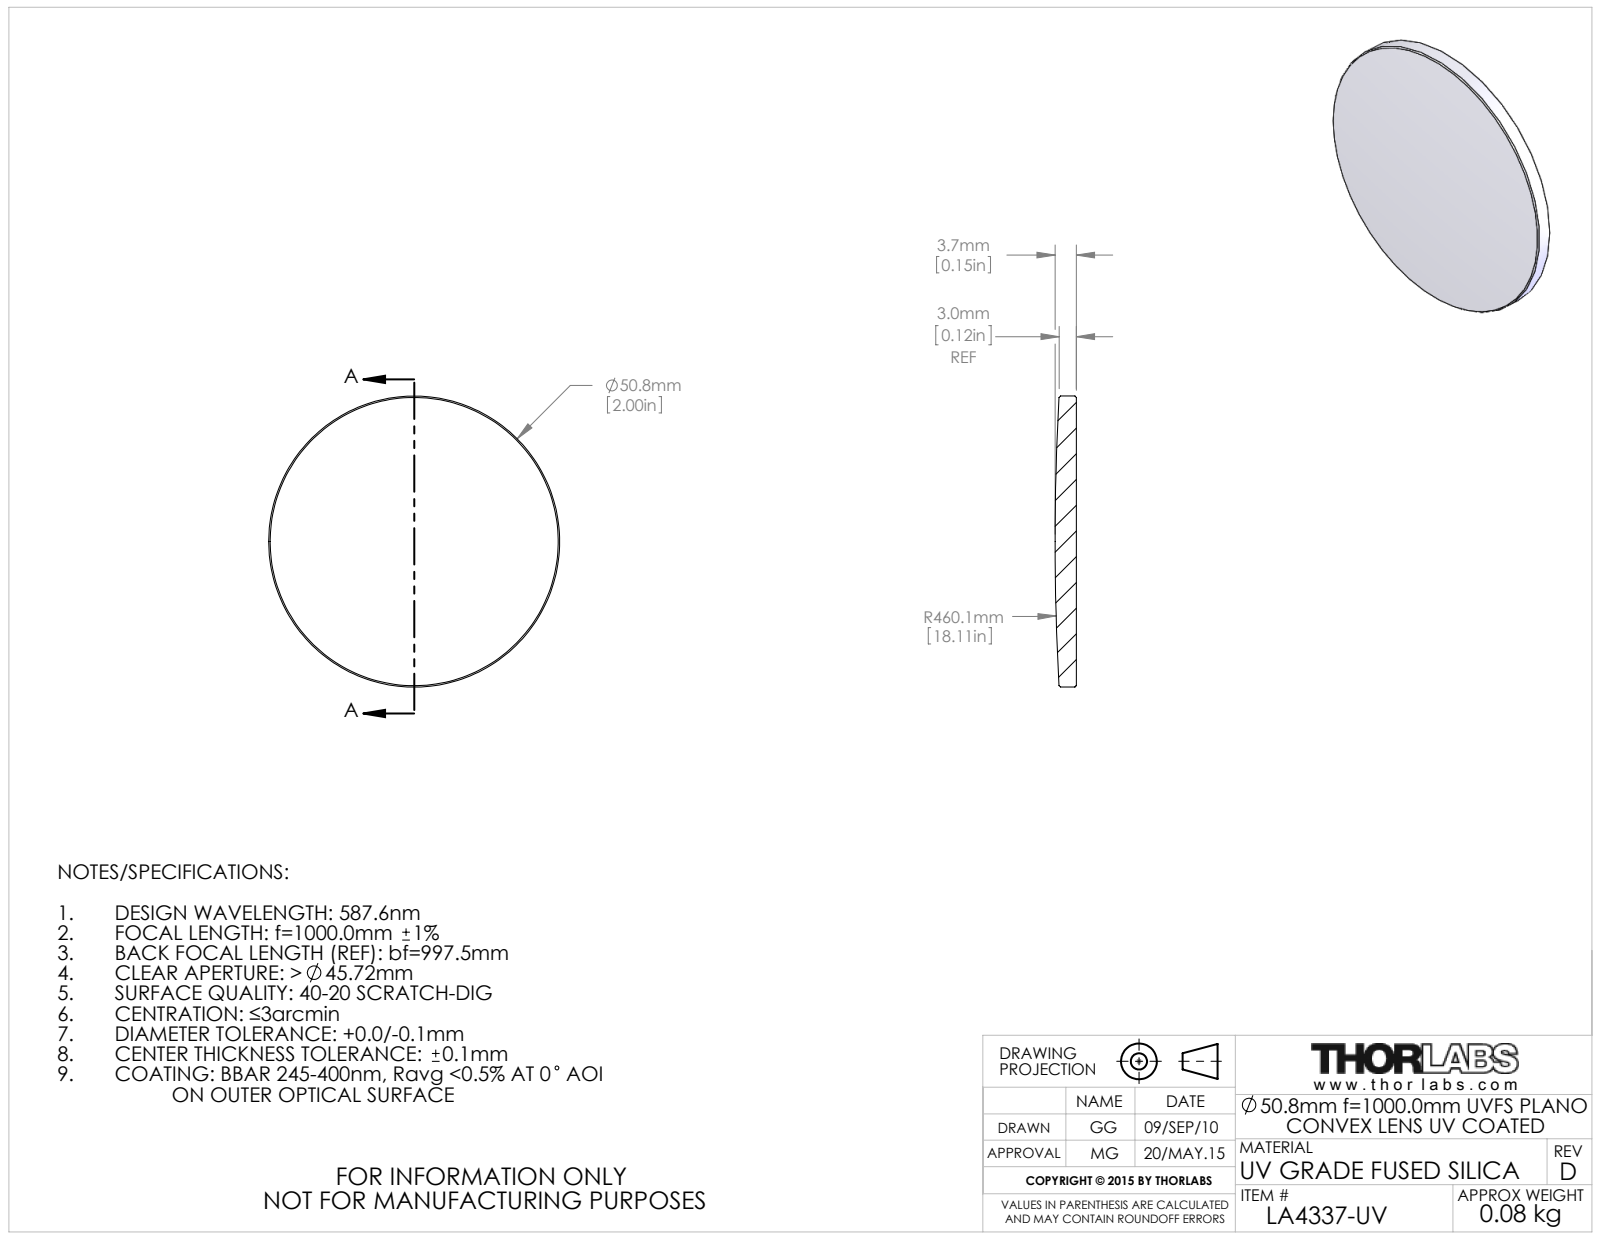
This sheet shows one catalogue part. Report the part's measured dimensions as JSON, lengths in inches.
{"part_name": "4301-E0W", "step_written_by": "SolidWorks 2014 (CONFIG_CONTROL_DESIGN)", "units": "inches", "bodies": {"solids": 1, "faces": 9, "planar": 1, "cylindrical": 2, "other": 6}, "overall_size": [2, 2, 0.146], "volume_in3": 0.414, "surface_area_in2": 6.958, "round_bosses_or_shafts": [[2, 1]]}
